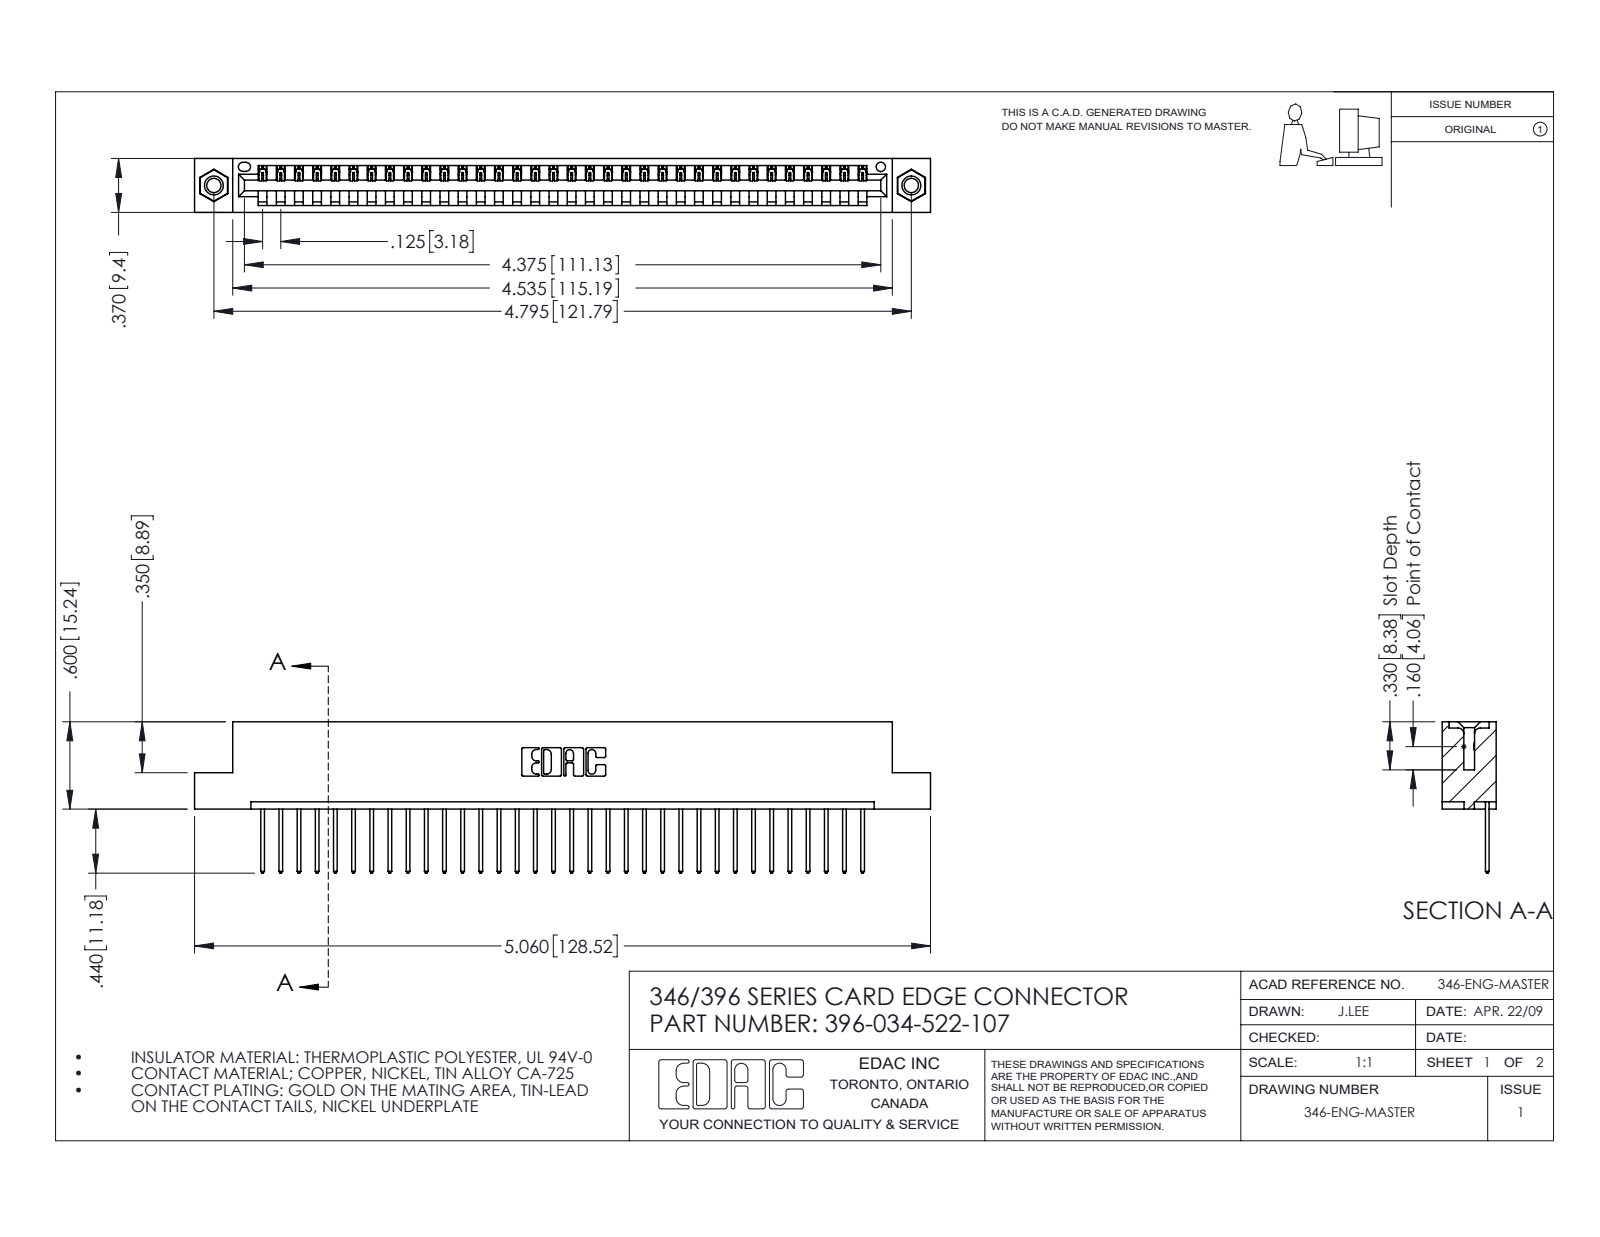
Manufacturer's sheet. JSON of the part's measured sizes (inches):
{"part_name": "345-250-001_345-250-005-103; 396-034-522-107; 345-292-001_345-293-122; 346 Part_Flush Mounting Lugs - 0.156 Dia-TI", "step_written_by": "SolidWorks 2016 (CONFIG_CONTROL_DESIGN)", "units": "inches", "bodies": {"solids": 37, "faces": 2154, "planar": 1468, "cylindrical": 670, "other": 16}, "overall_size": [5.06, 1.04, 0.37], "volume_in3": 0.747, "surface_area_in2": 23.82, "round_holes": [[0.098, 2], [0.125, 2], [0.156, 2], [0.064, 1]], "round_bosses_or_shafts": [[0.155, 2]], "partial_cylinders_radius": [[0.006, 68], [0.01, 68], [0.01, 22], [0.007, 6], [0.031, 6], [0.026, 3], [0.031, 2], [0.04, 2]], "face_to_face_distances": [0.048, 0.322, 0.37, 0.25, 0.072, 0.298, 0.025, 0.148, 0.222, 0.1], "hole_center_spacings": [0.246, 4.587, 4.795]}
